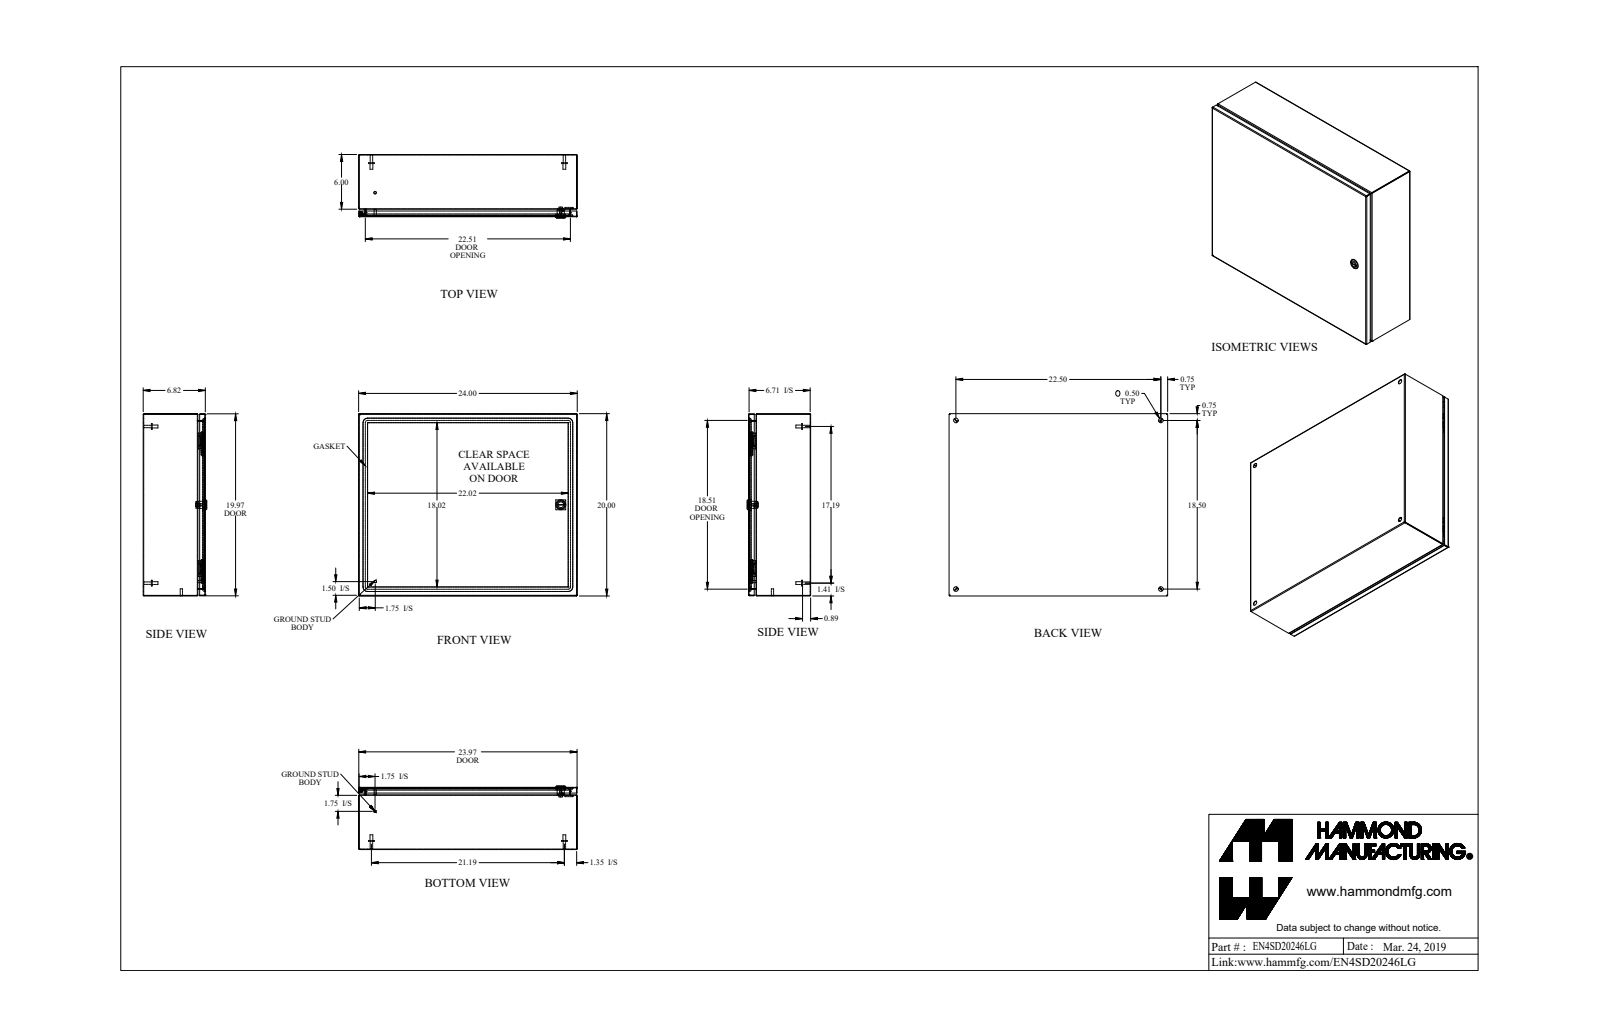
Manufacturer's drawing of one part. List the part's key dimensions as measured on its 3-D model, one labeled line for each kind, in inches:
Part name (STEP PRODUCT): EN4SD20246LG_Default
STEP written by: SolidWorks 2019 (CONFIG_CONTROL_DESIGN)
Units: inches
Bodies: 21 solids, 634 faces (285 planar, 213 cylindrical, 136 other)
Overall size (bounding box): 24 × 20 × 6.982
Volume: 103.2 in³ · Surface area: 3 513 in²
Round holes (diameter × count): ⌀0.5 ×4, ⌀0.172 ×1, ⌀0.232 ×1, ⌀0.24 ×1, ⌀0.242 ×1, ⌀0.625 ×1, ⌀0.785 ×1
Round bosses / shafts (diameter × count): ⌀0.625 ×4, ⌀0.313 ×4, ⌀0.27 ×4, ⌀0.281 ×2, ⌀0.25 ×2, ⌀1.1 ×1, ⌀0.525 ×1, ⌀0.455 ×1
Partial cylindrical surfaces — rounded edges, fillets, slot ends (radius × count): R0.029 ×21, R0.086 ×21, R0.25 ×16, R19 ×8, R0.006 ×4, R0.062 ×4, R0.499 ×4, R0.125 ×2
Main face-to-face distances: 0.057, 6.765, 6.708, 6.822, 19.943, 23.943, 19.886, 20, 23.886, 24
Hole centre spacings: 18.5, 22.5, 23.351, 29.129, 9.31, 9.311
